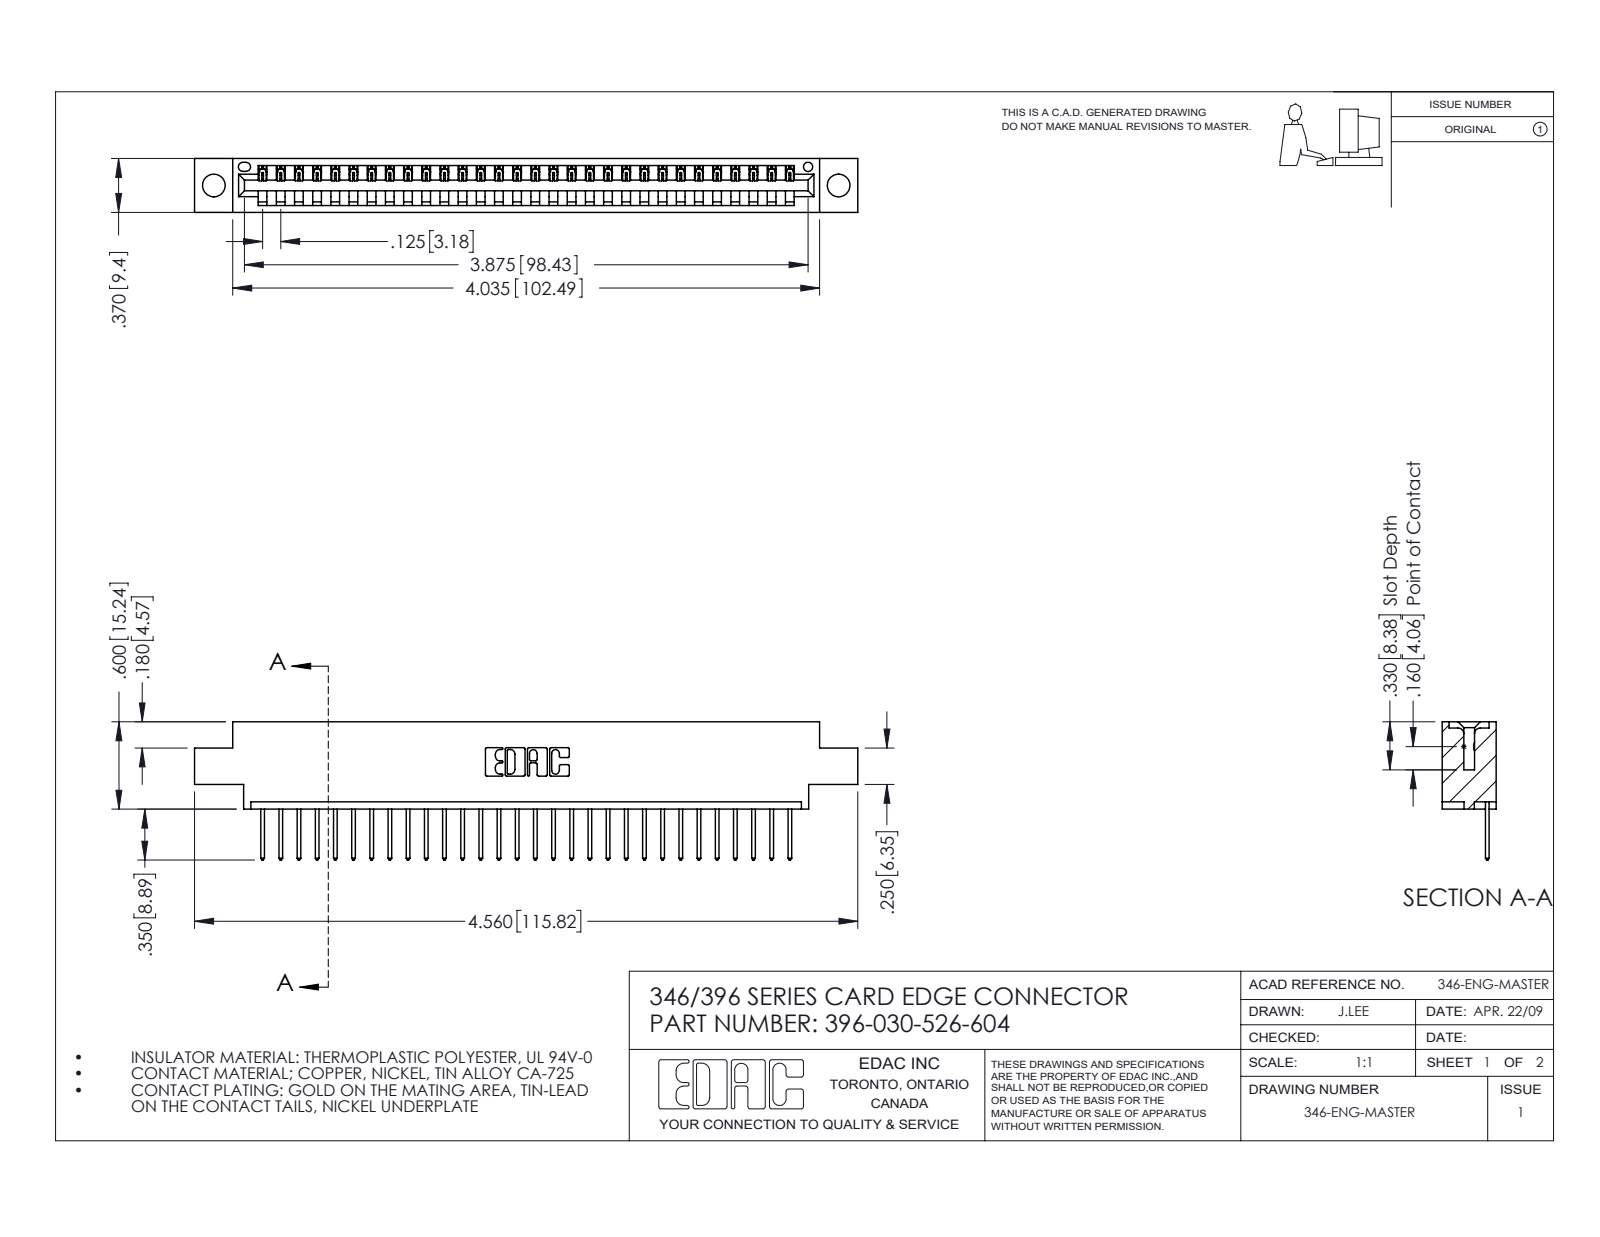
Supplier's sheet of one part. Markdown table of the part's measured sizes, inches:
| quantity | value |
| --- | --- |
| part name | 345-292-001_345-293-126; 396-030-526-604; 346 Part_0.170 Offset - 0.156 Dia-TH |
| STEP written by | SolidWorks 2016 (CONFIG_CONTROL_DESIGN) |
| units | inches |
| bodies | 31 solids, 1866 faces (1280 planar, 586 cylindrical, 0 other) |
| overall size | 4.56 × 0.95 × 0.37 |
| volume | 0.655 in³ |
| surface area | 20.5 in² |
| round holes (diameter × count) | 0.156 × 2, 0.064 × 1 |
| partial cylindrical surfaces (radius × count) | 0.006 × 60, 0.01 × 60, 0.01 × 22, 0.007 × 6, 0.031 × 6, 0.026 × 3, 0.031 × 2, 0.04 × 2 |
| main face-to-face distances | 0.048, 0.322, 0.37, 0.25, 0.072, 0.298, 0.025, 0.148, 0.222, 0.1 |
| hole center spacings | 0.246, 4.087, 4.295 |
